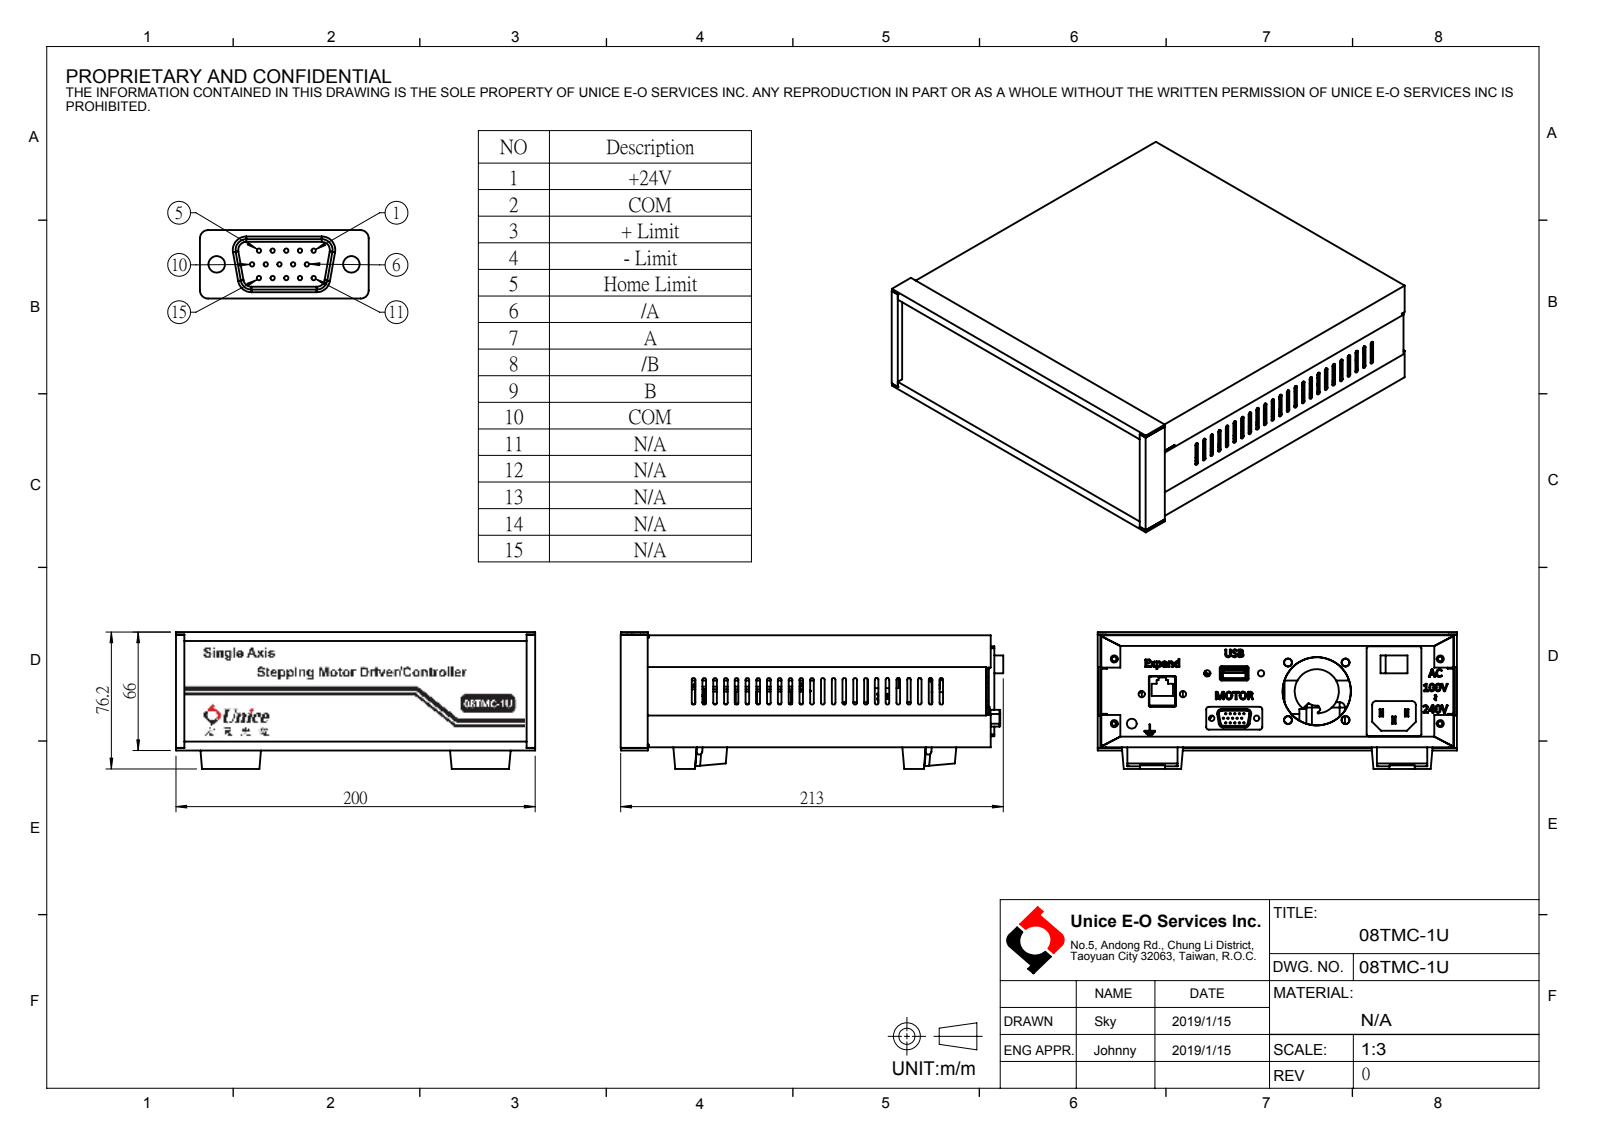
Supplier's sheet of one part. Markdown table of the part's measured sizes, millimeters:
| quantity | value |
| --- | --- |
| part name | 08TMC-1U |
| STEP written by | SolidWorks 2016 (AUTOMOTIVE_DESIGN) |
| units | millimeters |
| bodies | 0 solids, 773 faces (471 planar, 269 cylindrical, 33 other) |
| overall size | 213 × 200 × 76.2 |
| round holes (diameter × count) | 0.8 × 15, 3.5 × 8, 2.5 × 6, 4 × 6, 4.3 × 4, 4.5 × 4, 3.05 × 2, 4.2 × 2, 5 × 1, 5.5 × 1, 12 × 1, 37.99 × 1 |
| partial cylindrical surfaces (radius × count) | 1 × 56, 1.5 × 12, 0.5 × 8, 2 × 8, 0.2 × 5, 3.15 × 4, 0.6 × 3, 1.65 × 2 |
| main face-to-face distances | 1, 61.4, 6.2, 55.2, 60.4, 62.4, 7.2, 5.2, 56.2, 54.2 |
| hole center spacings | 2.84, 5.08, 4.58, 2.54, 5.68, 6.84, 7.18, 7.62 |
